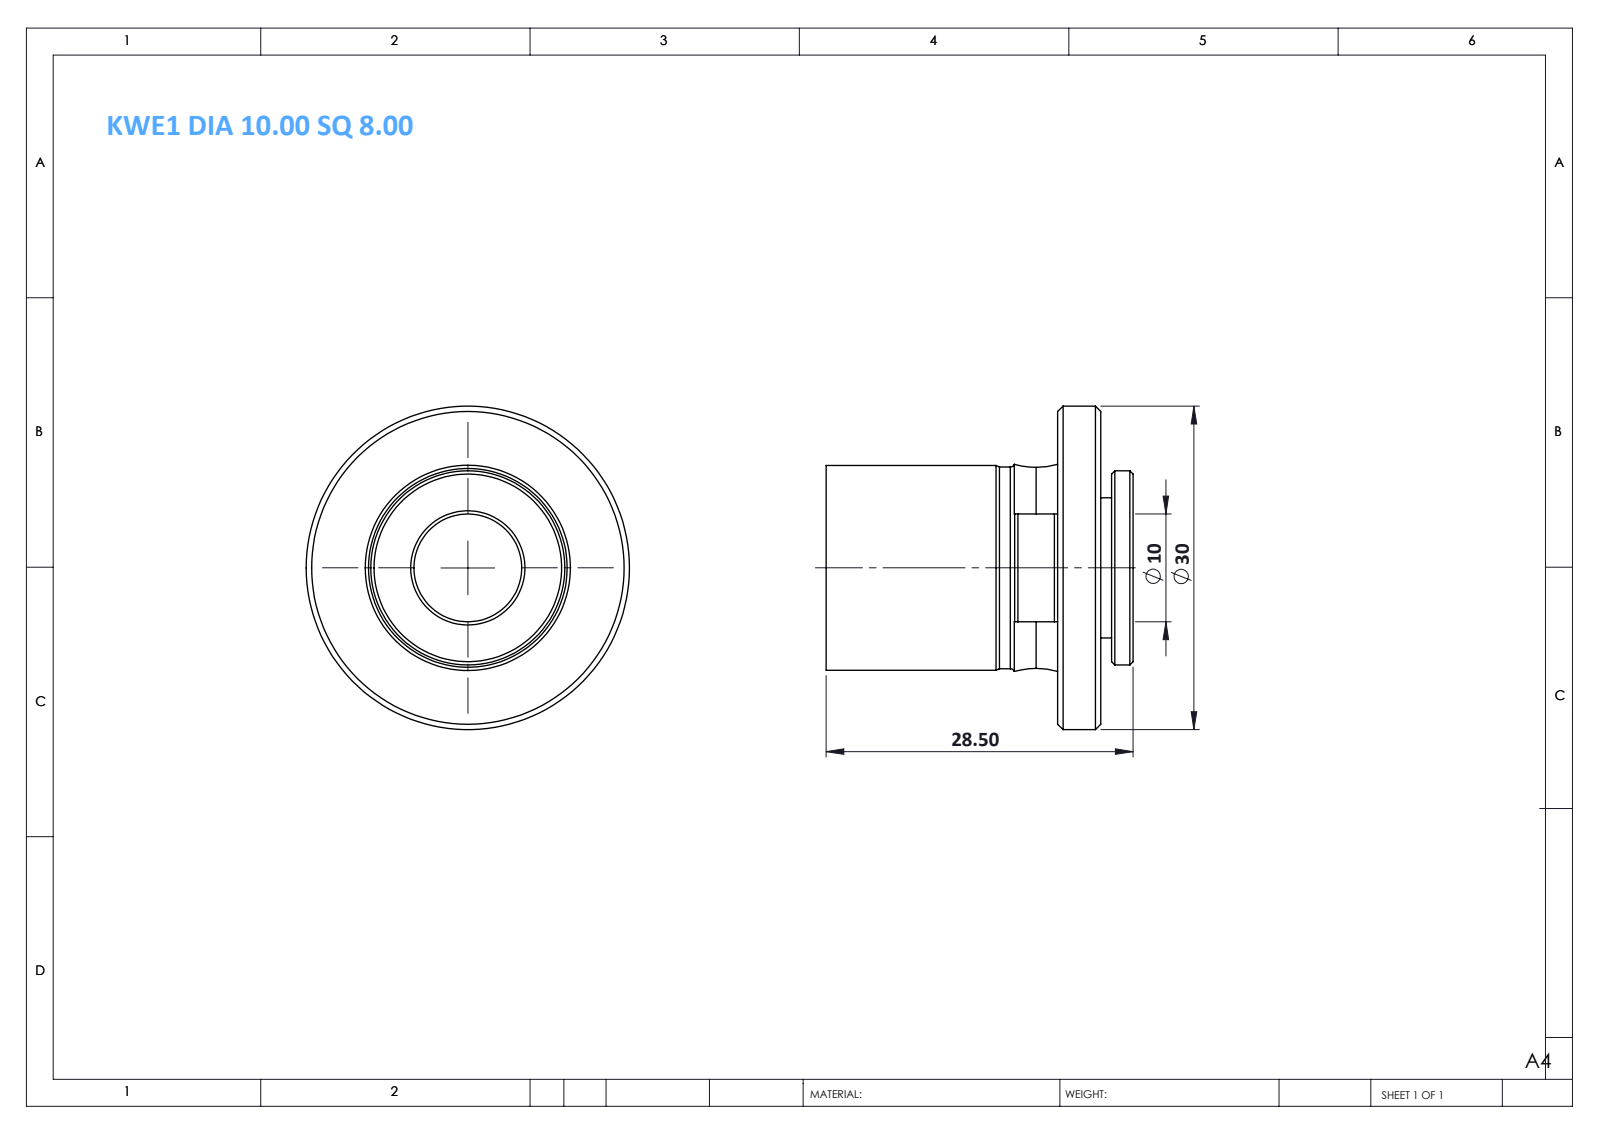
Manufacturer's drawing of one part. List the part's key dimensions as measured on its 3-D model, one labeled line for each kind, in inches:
Part name (STEP PRODUCT): KWE1 DIA 10.00 SQ 8.00
STEP written by: SolidWorks 2014 (CONFIG_CONTROL_DESIGN)
Units: inches
Bodies: 1 solid, 57 faces (13 planar, 16 cylindrical, 28 other)
Overall size (bounding box): 1.181 × 1.181 × 1.122
Volume: 0.522 in³ · Surface area: 6.073 in²
Round holes (diameter × count): ⌀0.394 ×1, ⌀0.75 ×1
Round bosses / shafts (diameter × count): ⌀1.181 ×1, ⌀0.748 ×1, ⌀0.736 ×1, ⌀0.709 ×1, ⌀0.512 ×1
Partial cylindrical surfaces — rounded edges, fillets, slot ends (radius × count): R0.488 ×1
Main face-to-face distances: 0.157, 0.846, 1.004, 1.122, 0.276, 0.118, 0.315, 1.043, 0.197, 0.039
